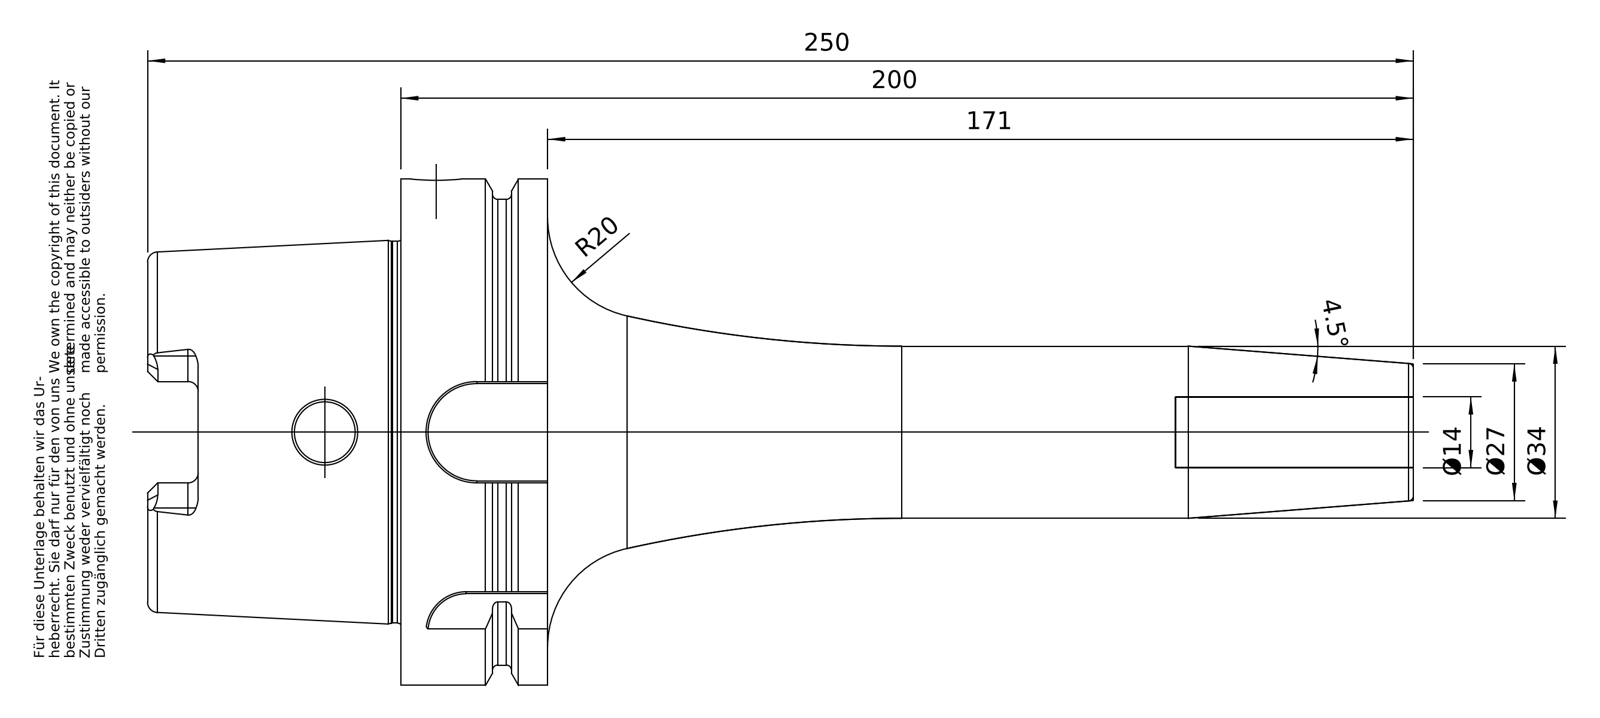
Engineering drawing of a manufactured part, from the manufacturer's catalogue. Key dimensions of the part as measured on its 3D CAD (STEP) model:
Part name (STEP PRODUCT): A100-146-14
STEP written by: PRO/ENGINEER BY PARAMETRIC TECHNOLOGY CORPORATION, 2010430 (CONFIG_CONTROL_DESIGN)
Units: millimetres
Bodies: 1 solid, 176 faces (50 planar, 51 cylindrical, 75 other)
Overall size (bounding box): 250 × 100 × 100
Volume: 432 329 mm³ · Surface area: 69 274 mm²
Round holes (diameter × count): ⌀10 ×1, ⌀12 ×1, ⌀14 ×1, ⌀22.5 ×1, ⌀24 ×1, ⌀24.32 ×1, ⌀24.5 ×1, ⌀53 ×1, ⌀63 ×1
Round bosses / shafts (diameter × count): ⌀100 ×1, ⌀92 ×1, ⌀75.36 ×1, ⌀34 ×1
Partial cylindrical surfaces — rounded edges, fillets, slot ends (radius × count): R2 ×6, R5 ×4, R8 ×1, R10 ×1, R11 ×1
Main face-to-face distances: 29, 12.5, 16.5, 50, 62.5, 79, 88, 78.5, 28.5, 16
